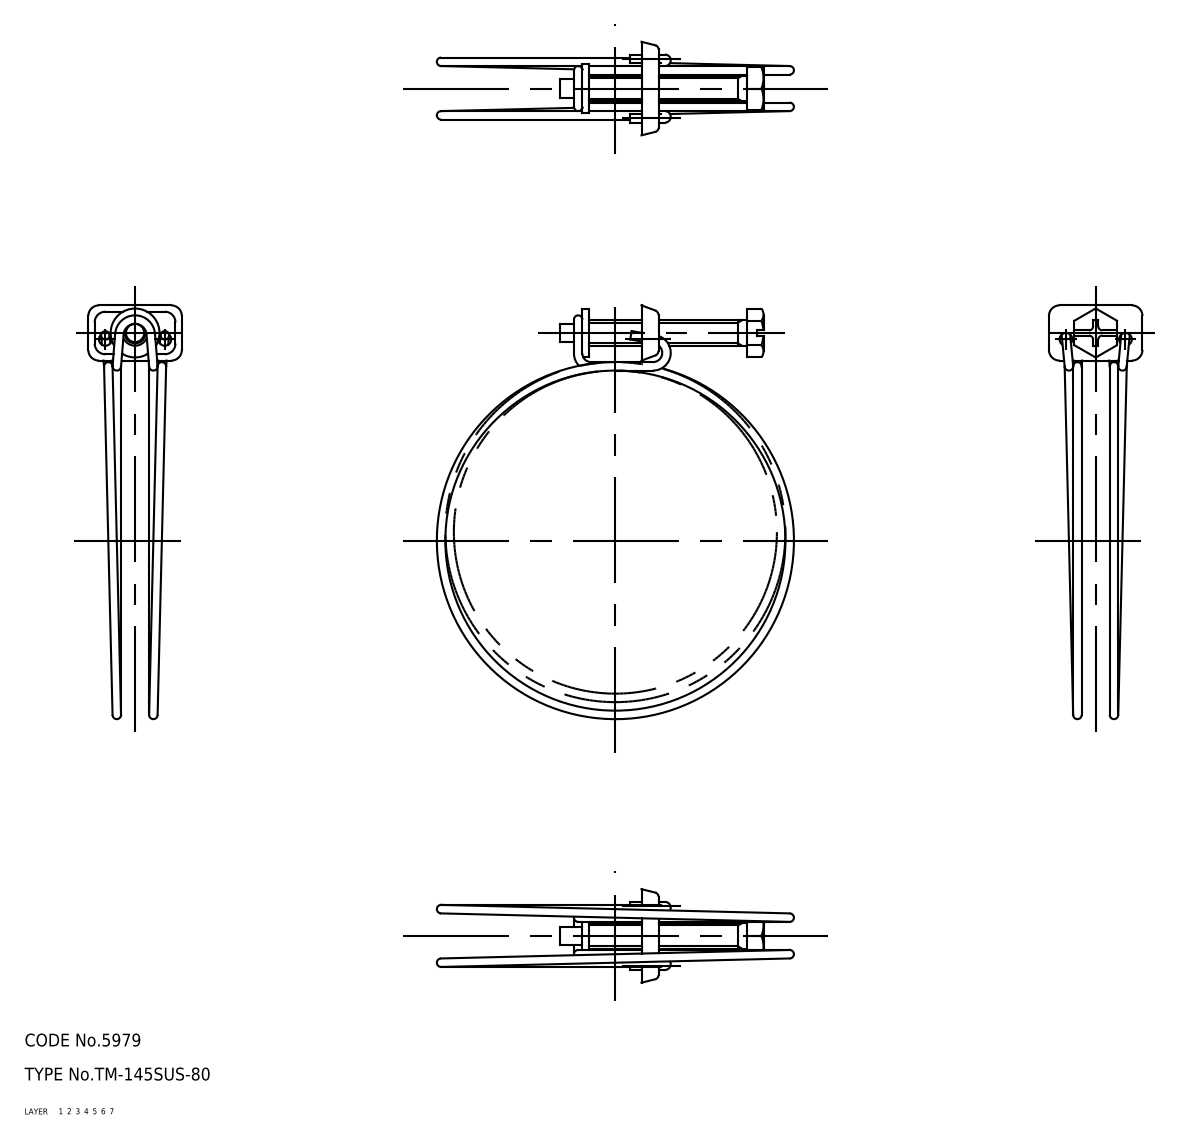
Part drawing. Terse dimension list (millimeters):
name: screw; holder; band; TM_145SUS_80_22889_36
written by: CADfix (AUTOMOTIVE_DESIGN)
unit: mm
bodies: 3 solids, 119 faces (0 planar, 0 cylindrical, 119 other)
size: 97.35 × 84 × 22
volume: 4 005 mm³; area: 5 942 mm²
